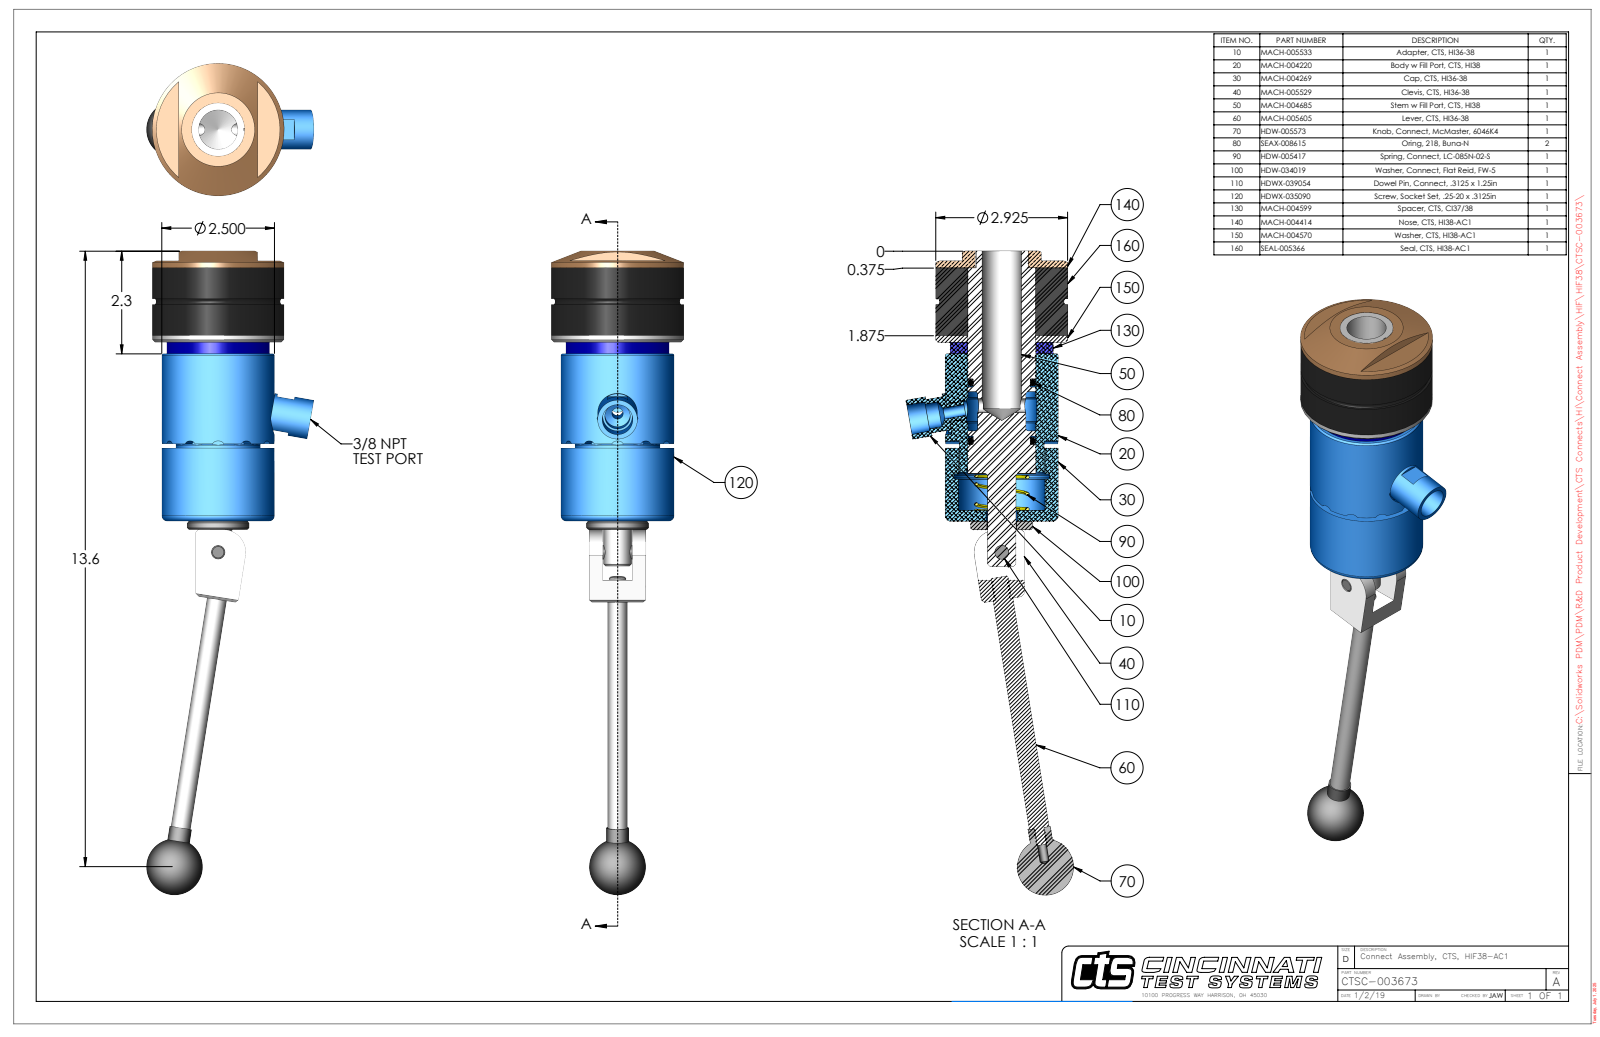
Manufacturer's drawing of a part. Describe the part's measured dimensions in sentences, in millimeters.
The part is named "CTSC-003673". Its 3-D file was written by "SolidWorks 2023 (AUTOMOTIVE_DESIGN)". It is 10 solids with 316 faces: 111 planar, 130 cylindrical and 75 other. Overall it measures 362.6 by 94.4 by 74.3 millimeters. Its volume is 548 100 cubic millimeters and its surface area 106 800 square millimeters. Round holes: 2 of diameter 5.1, 1 of diameter 3.8, 1 of diameter 6.4, 1 of diameter 7.9, 1 of diameter 7.9, 1 of diameter 8, 1 of diameter 8, 1 of diameter 14.3, 1 of diameter 16.7, 1 of diameter 17.7, 1 of diameter 22.2, 1 of diameter 29.8. Round bosses or shafts: 1 of diameter 74.3, 1 of diameter 74.3, 1 of diameter 63.5, 1 of diameter 57.9, 1 of diameter 47.6, 1 of diameter 38.1, 1 of diameter 38, 1 of diameter 35.1. Partial cylindrical surfaces (rounded edges, fillets, slot ends): 12 of radius 3, 2 of radius 0.7, 1 of radius 4.8, 1 of radius 5, 1 of radius 11.9, 1 of radius 12, 1 of radius 12.7, 1 of radius 30.4. The main face-to-face distances are 38.1, 3.9, 42, 6.4, 10.2, 48.3, 94.3, 100.7, 104.5, 142.6. The hole center spacings are 18.8, 53.8, 72.6.
